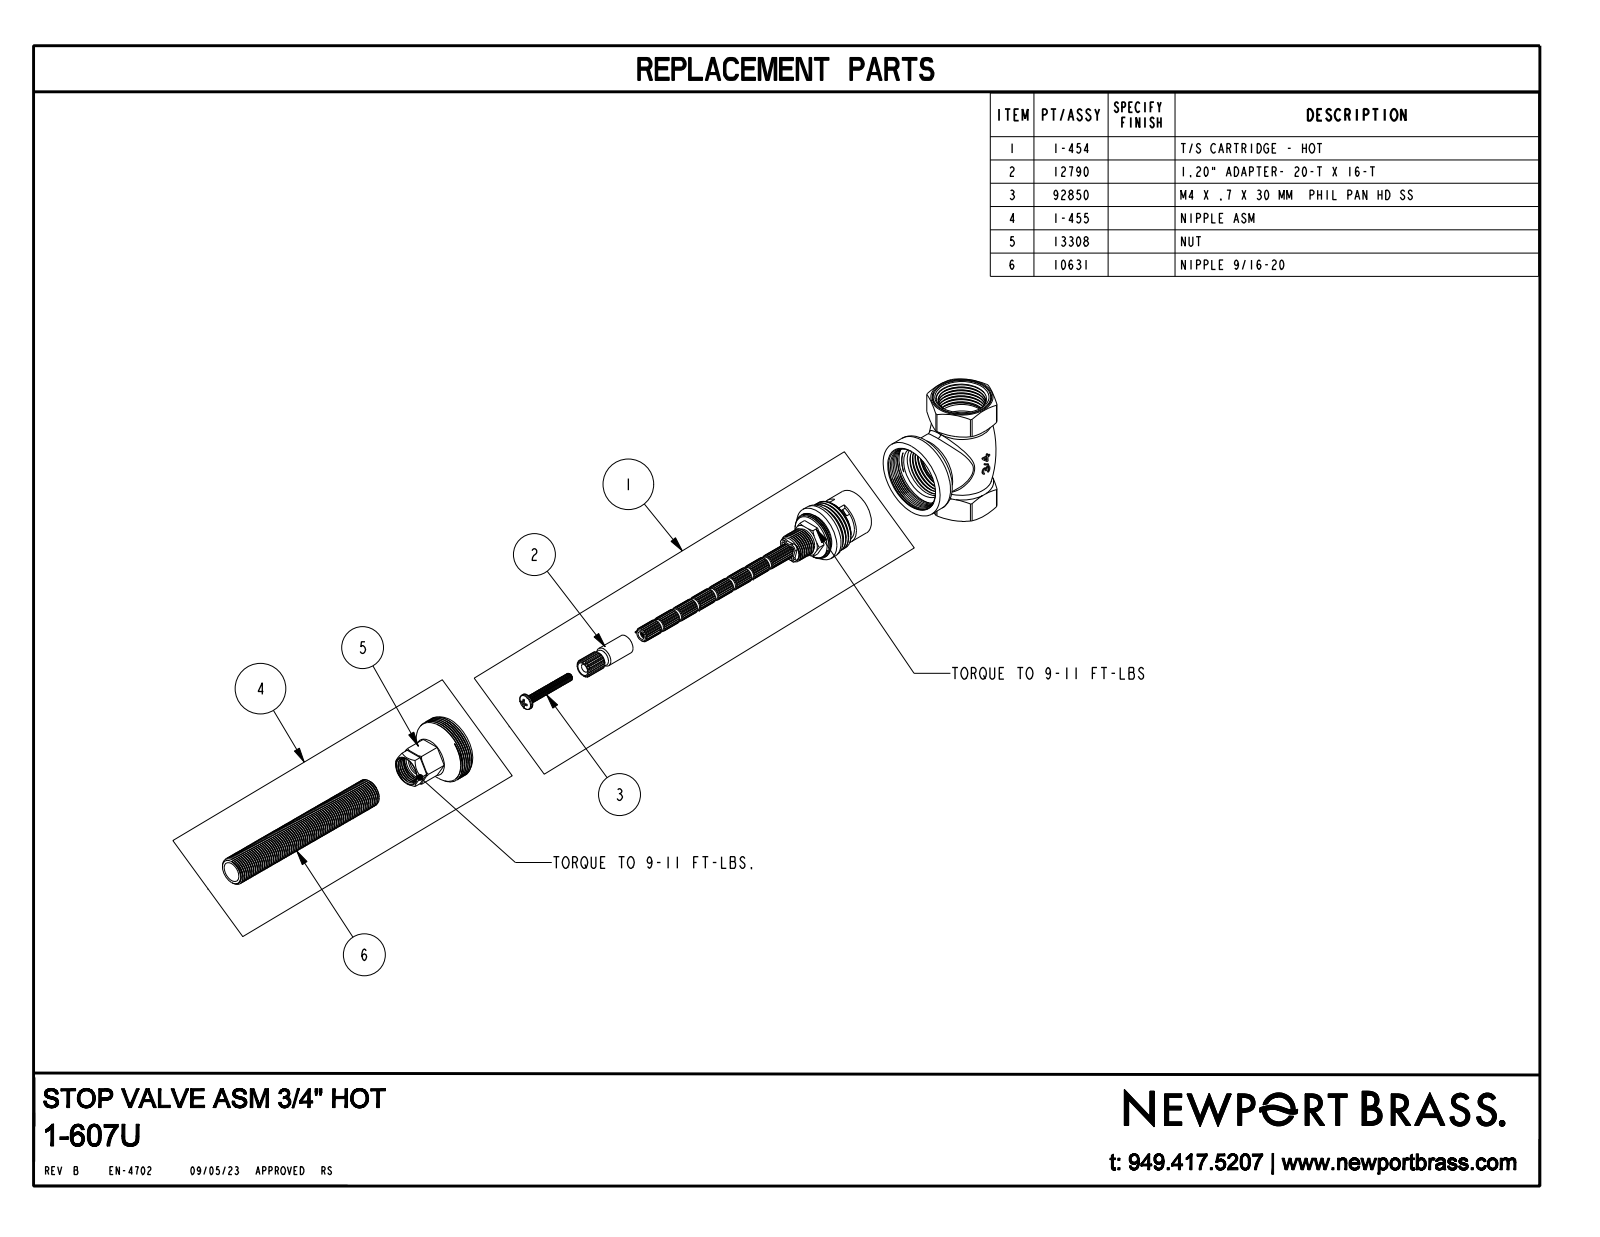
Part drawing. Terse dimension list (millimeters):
name: 1-607U
written by: CREO PARAMETRIC BY PTC INC, 2018400 (AUTOMOTIVE_DESIGN)
unit: mm
bodies: 1 solid, 756 faces (259 planar, 351 cylindrical, 146 other)
size: 190.8 × 64.8 × 40.1
volume: 97 010 mm³; area: 21 140 mm²
holes: 1× ⌀4.4, 1× ⌀8.4
bosses: 1× ⌀40.1, 1× ⌀31, 1× ⌀25.8, 1× ⌀14.3, 1× ⌀9.9, 1× ⌀8.3, 1× ⌀8, 1× ⌀4
rounds: 1× R3.5, 1× R4.2, 1× R4.7, 1× R18
face distances: 31.6, 64.8, 17, 0.6, 16.4, 23.9, 40.9, 15.8, 3.7, 114.2
